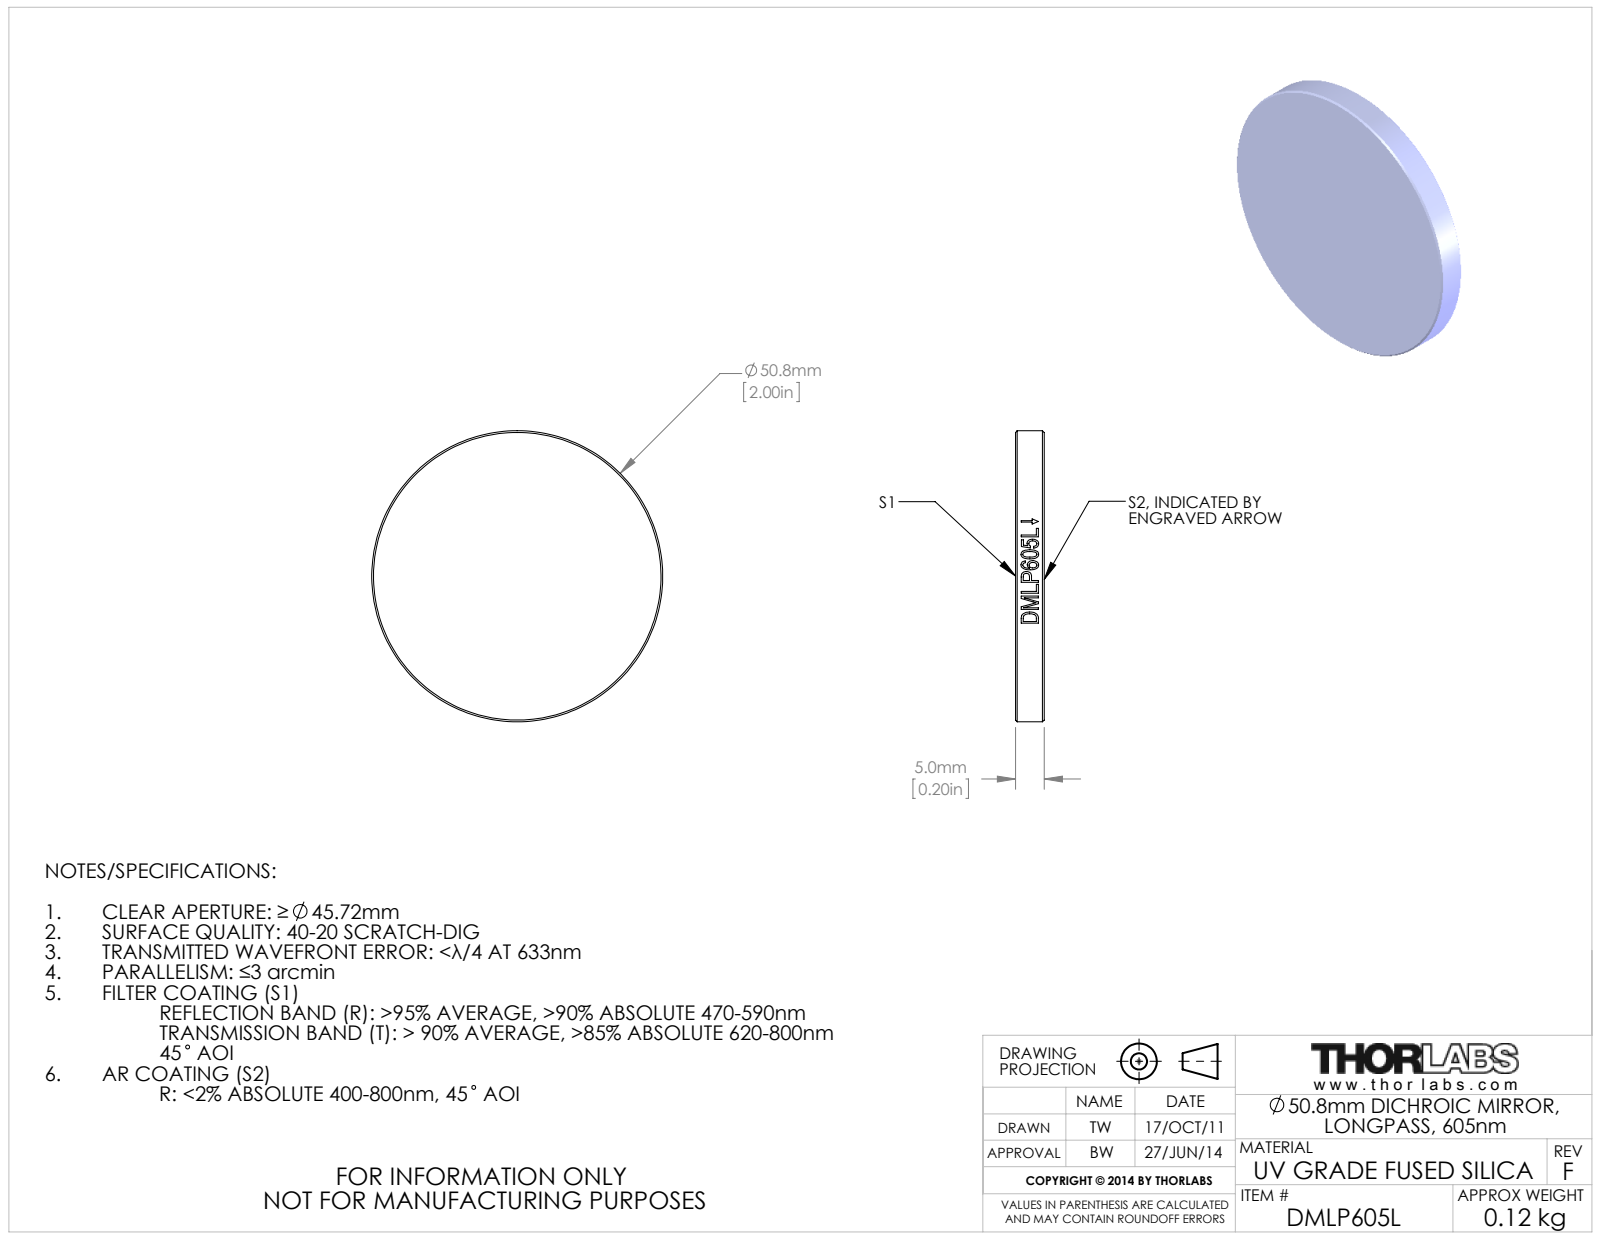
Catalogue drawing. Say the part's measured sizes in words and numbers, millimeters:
The part is named "21029-E0W". Its 3-D file was written by "SolidWorks 2011 (CONFIG_CONTROL_DESIGN)". It is 0 solids with 21 faces: 2 planar, 15 cylindrical and 4 other. Overall it measures 50.8 by 50.8 by 5 millimeters. Round bosses or shafts: 1 of diameter 50.8. The main face-to-face distances are 5.
